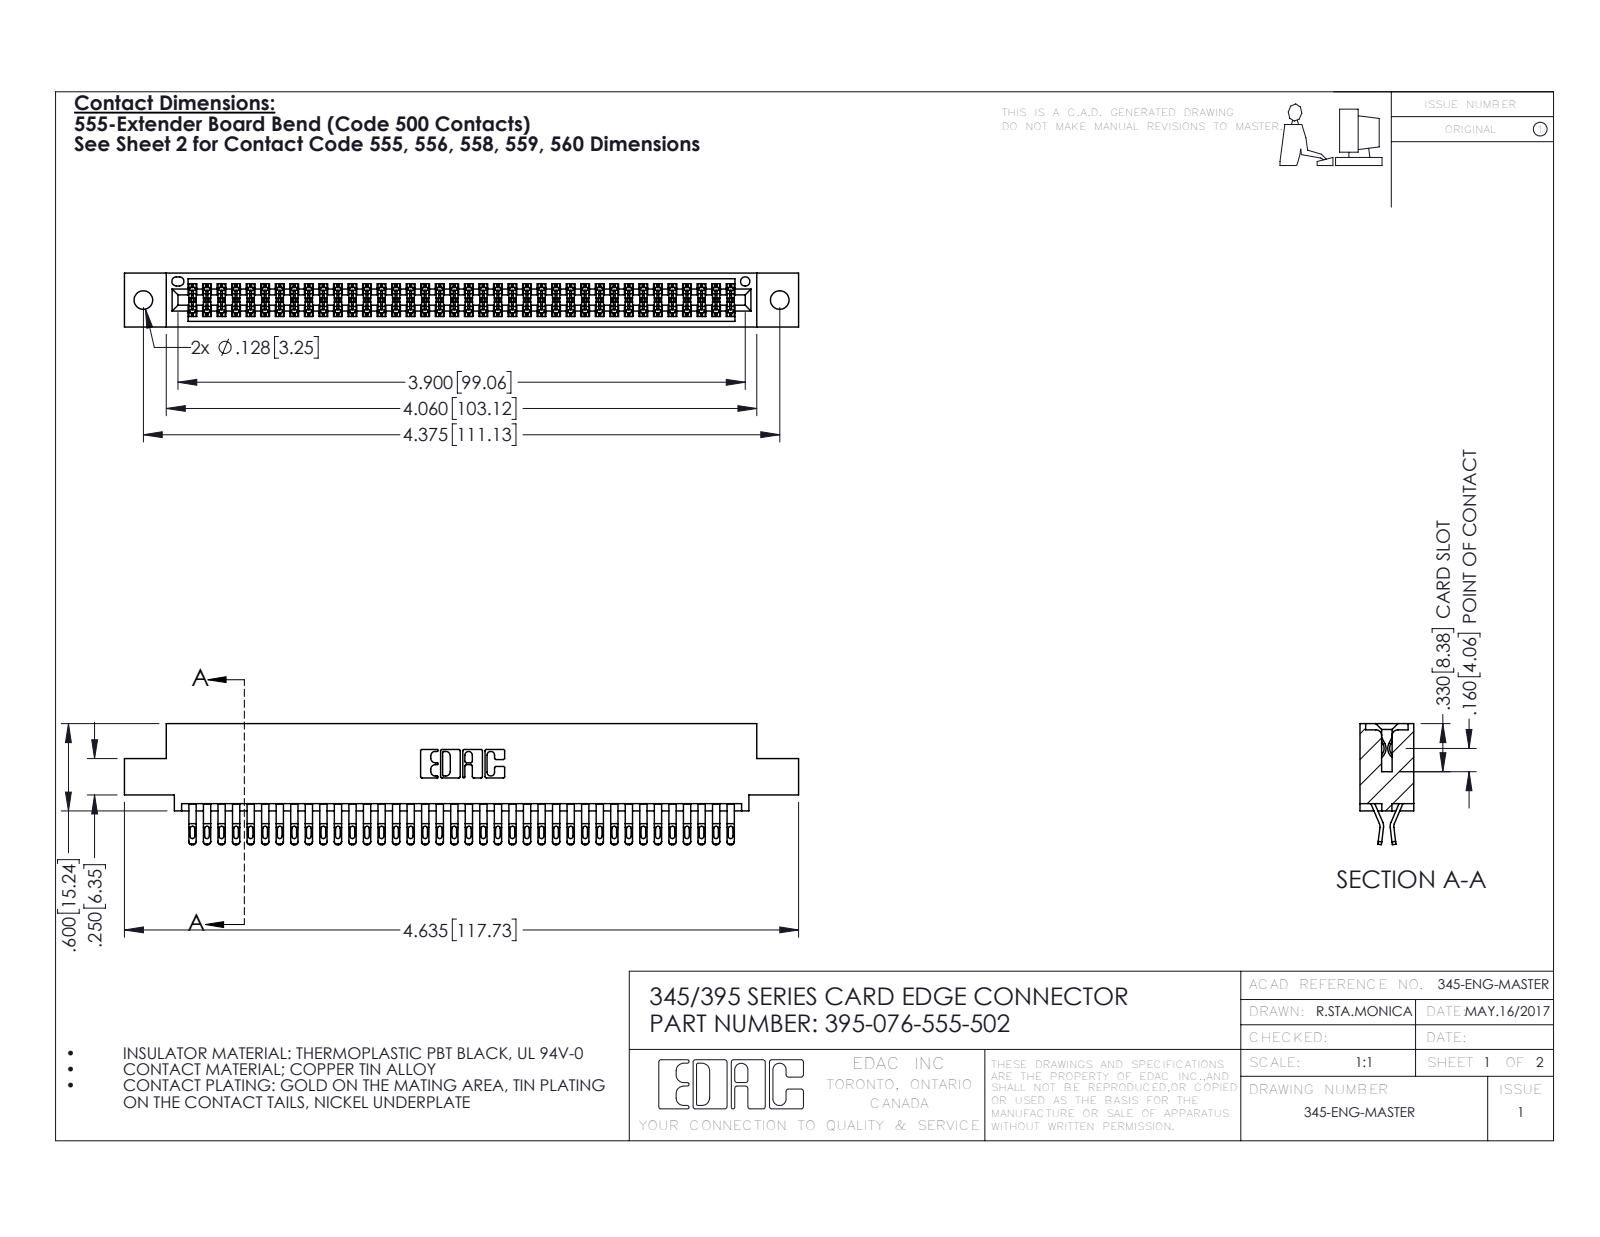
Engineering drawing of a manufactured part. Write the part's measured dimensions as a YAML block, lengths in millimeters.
part_name: "345 Part_0.110 Offset - 0.128 Dia; 345-292-001_555 Tail; 395-076-555-502"
step_written_by: "SolidWorks 2016 (CONFIG_CONTROL_DESIGN)"
units: millimeters
bodies: {solids: 77, faces: 4386, planar: 2440, cylindrical: 1946, other: 0}
overall_size: [117.7, 21.1, 9.4]
volume: 11500
surface_area: 17520
round_holes:
  - {diameter: 3.3, count: 2}
  - {diameter: 1.6, count: 1}
partial_cylinders:
  - {radius: 0.4, count: 190}
  - {radius: 0.5, count: 152}
  - {radius: 0.2, count: 114}
  - {radius: 0.3, count: 22}
  - {radius: 0.2, count: 6}
  - {radius: 0.8, count: 6}
  - {radius: 0.7, count: 3}
  - {radius: 0.3, count: 2}
face_to_face_distances: [7.6, 1.8, 0.6, 9.4, 5.1, 2.5, 6.9, 5.7, 4.4, 3.8]
hole_center_spacings: [6.9, 105.1, 111.1]
